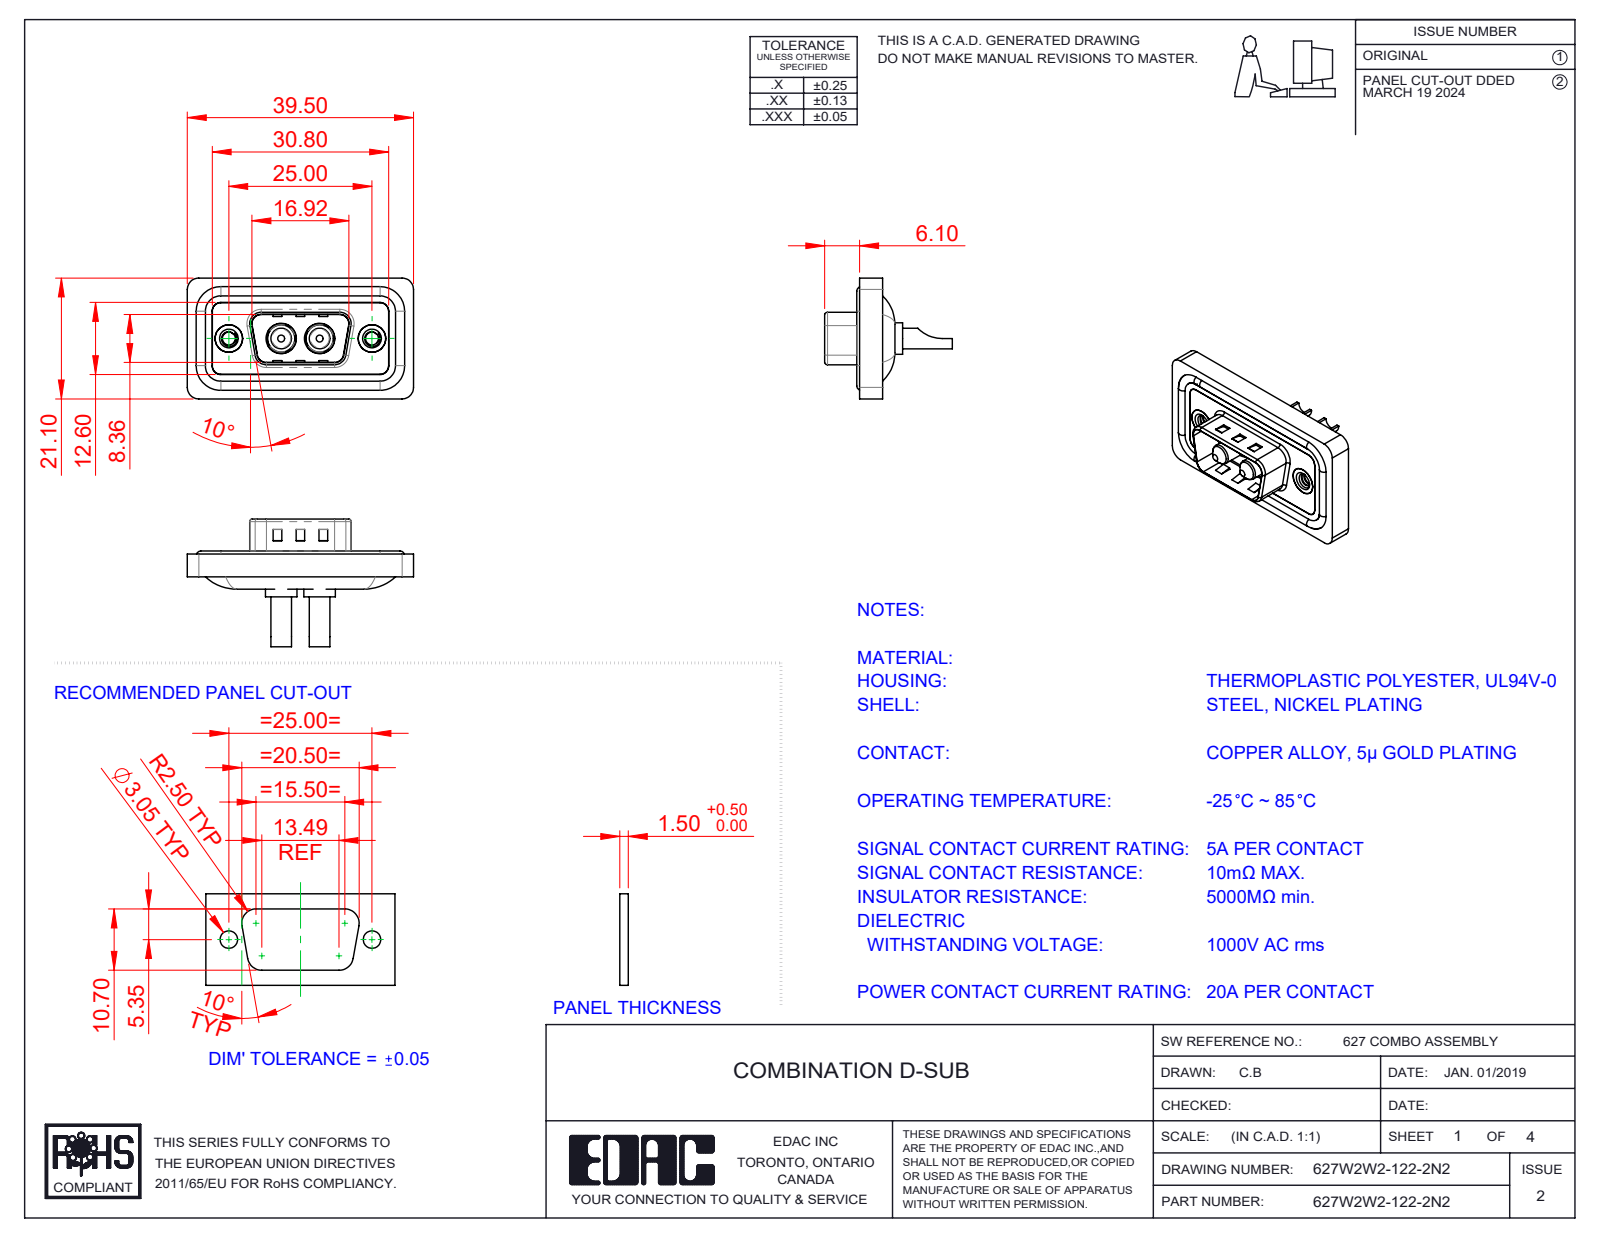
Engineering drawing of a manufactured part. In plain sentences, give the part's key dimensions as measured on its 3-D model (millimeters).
The part is named "627W2W2-122-2N2; 627Combo Shell Front_09 Contacts; 627Combo Threaded Rivet_2; 627Combo Waterproof Housing_09 Contacts (+3 more)". Its 3-D file was written by "SolidWorks 2023 (CONFIG_CONTROL_DESIGN)". It is 11 solids with 501 faces: 171 planar, 224 cylindrical and 106 other. Overall it measures 39.5 by 22.3 by 21.1 millimeters. Its volume is 4 486 cubic millimeters and its surface area 7 149 square millimeters. Round holes: 2 of diameter 2.26, 2 of diameter 2.7, 2 of diameter 4, 2 of diameter 4.8, 2 of diameter 4.85, 2 of diameter 5, 2 of diameter 5.3. Round bosses or shafts: 4 of diameter 1.6, 2 of diameter 5.5, 2 of diameter 5.2, 2 of diameter 4.9, 2 of diameter 4.75, 2 of diameter 3.75, 2 of diameter 3.6. Partial cylindrical surfaces (rounded edges, fillets, slot ends): 22 of radius 1.5, 18 of radius 2, 8 of radius 0.5, 8 of radius 1.6, 4 of radius 0.25, 4 of radius 0.6, 4 of radius 0.65, 4 of radius 0.9. The main face-to-face distances are 0.4, 1.1, 2.9, 3.1, 0.5, 1.6, 1.5, 4, 2.5, 0.7. The hole center spacings are 9.14, 15.86, 6.72, 25.
